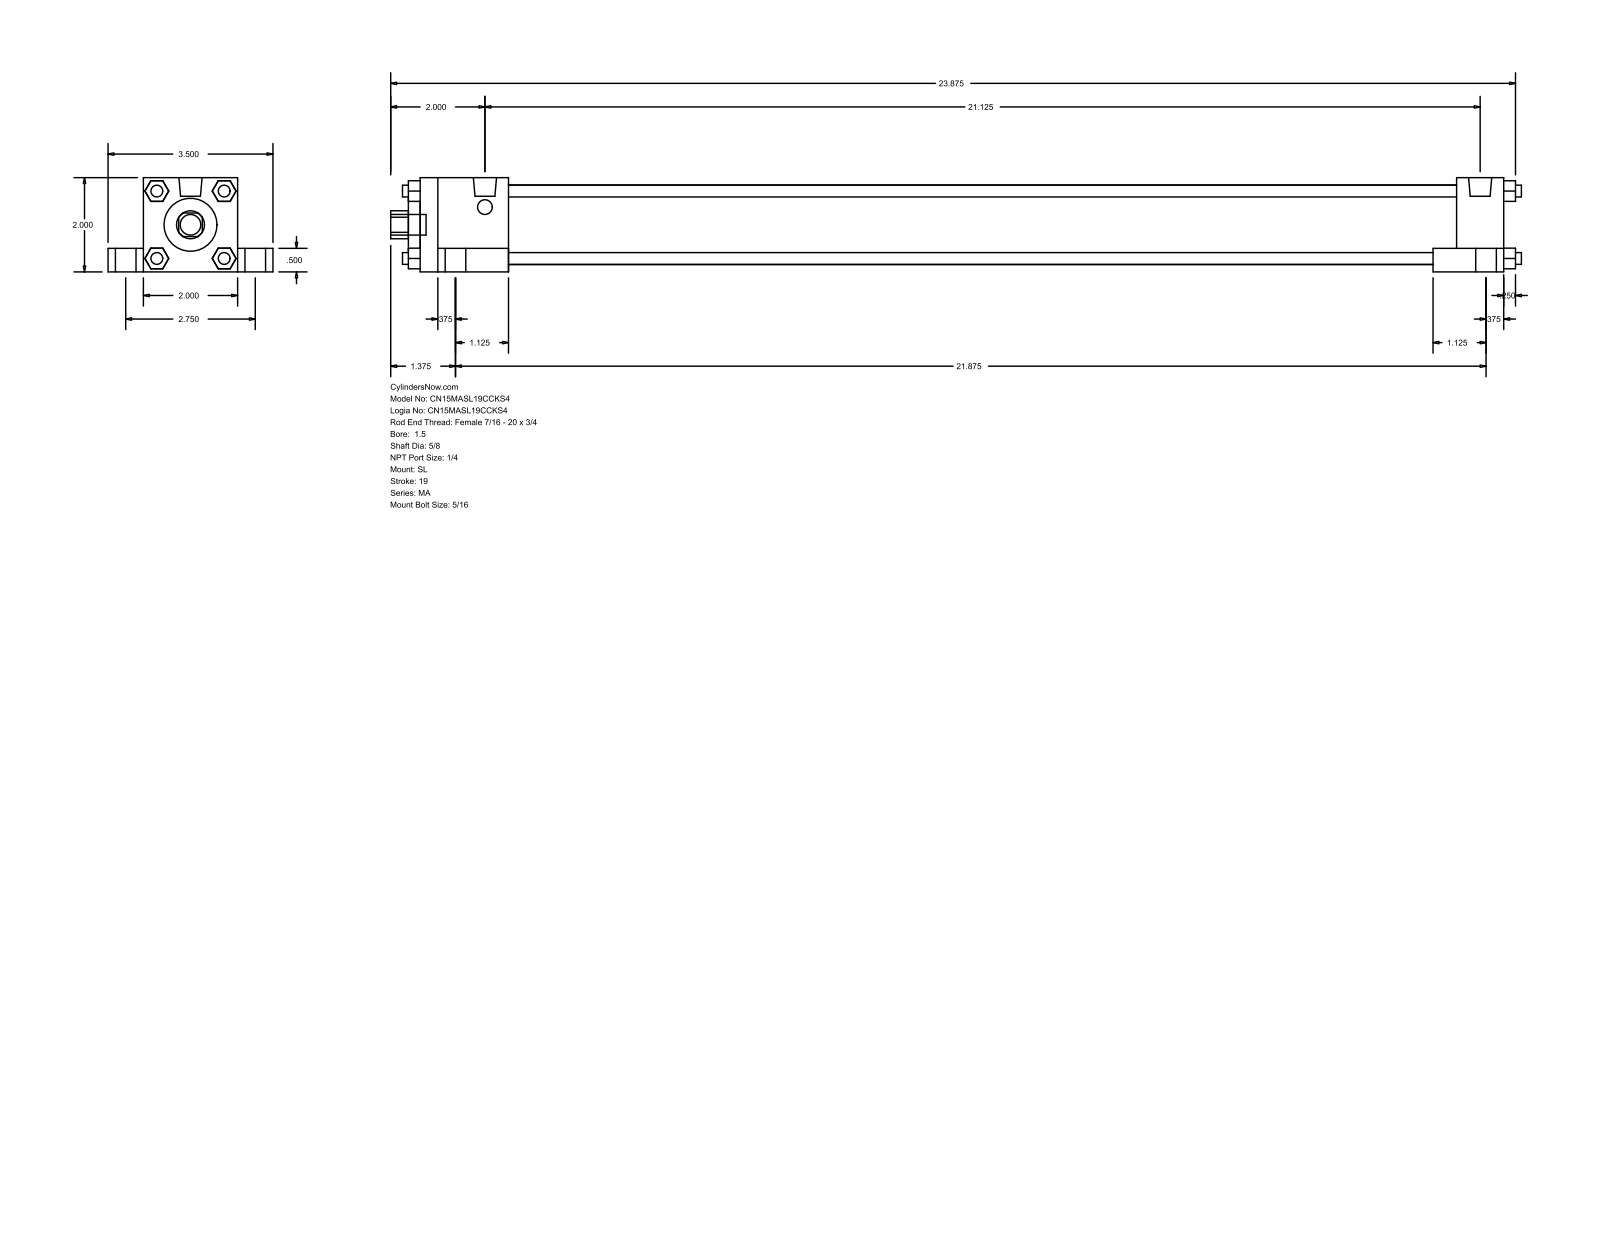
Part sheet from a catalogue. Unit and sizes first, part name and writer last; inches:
Units: inches
Overall size (bounding box): 24 × 3.5 × 2
Round holes (diameter × count): ⌀0.625 ×1, ⌀1.125 ×1, ⌀1.69 ×1
Round bosses / shafts (diameter × count): ⌀0.437 ×5, ⌀0.687 ×4, ⌀0.313 ×4, ⌀0.25 ×4, ⌀0.492 ×2
Partial cylindrical surfaces — rounded edges, fillets, slot ends (radius × count): R0.297 ×1
Main face-to-face distances: 2, 0.75, 1.5, 0.5, 23, 2.75, 20.125, 0.375, 22, 1
Bodies: 0 solids, 148 faces (112 planar, 36 cylindrical, 0 other)
Part name (STEP PRODUCT): MA_SL__0150_0.625
STEP written by: GSSL Pune (CONFIG_CONTROL_DESIGN)
